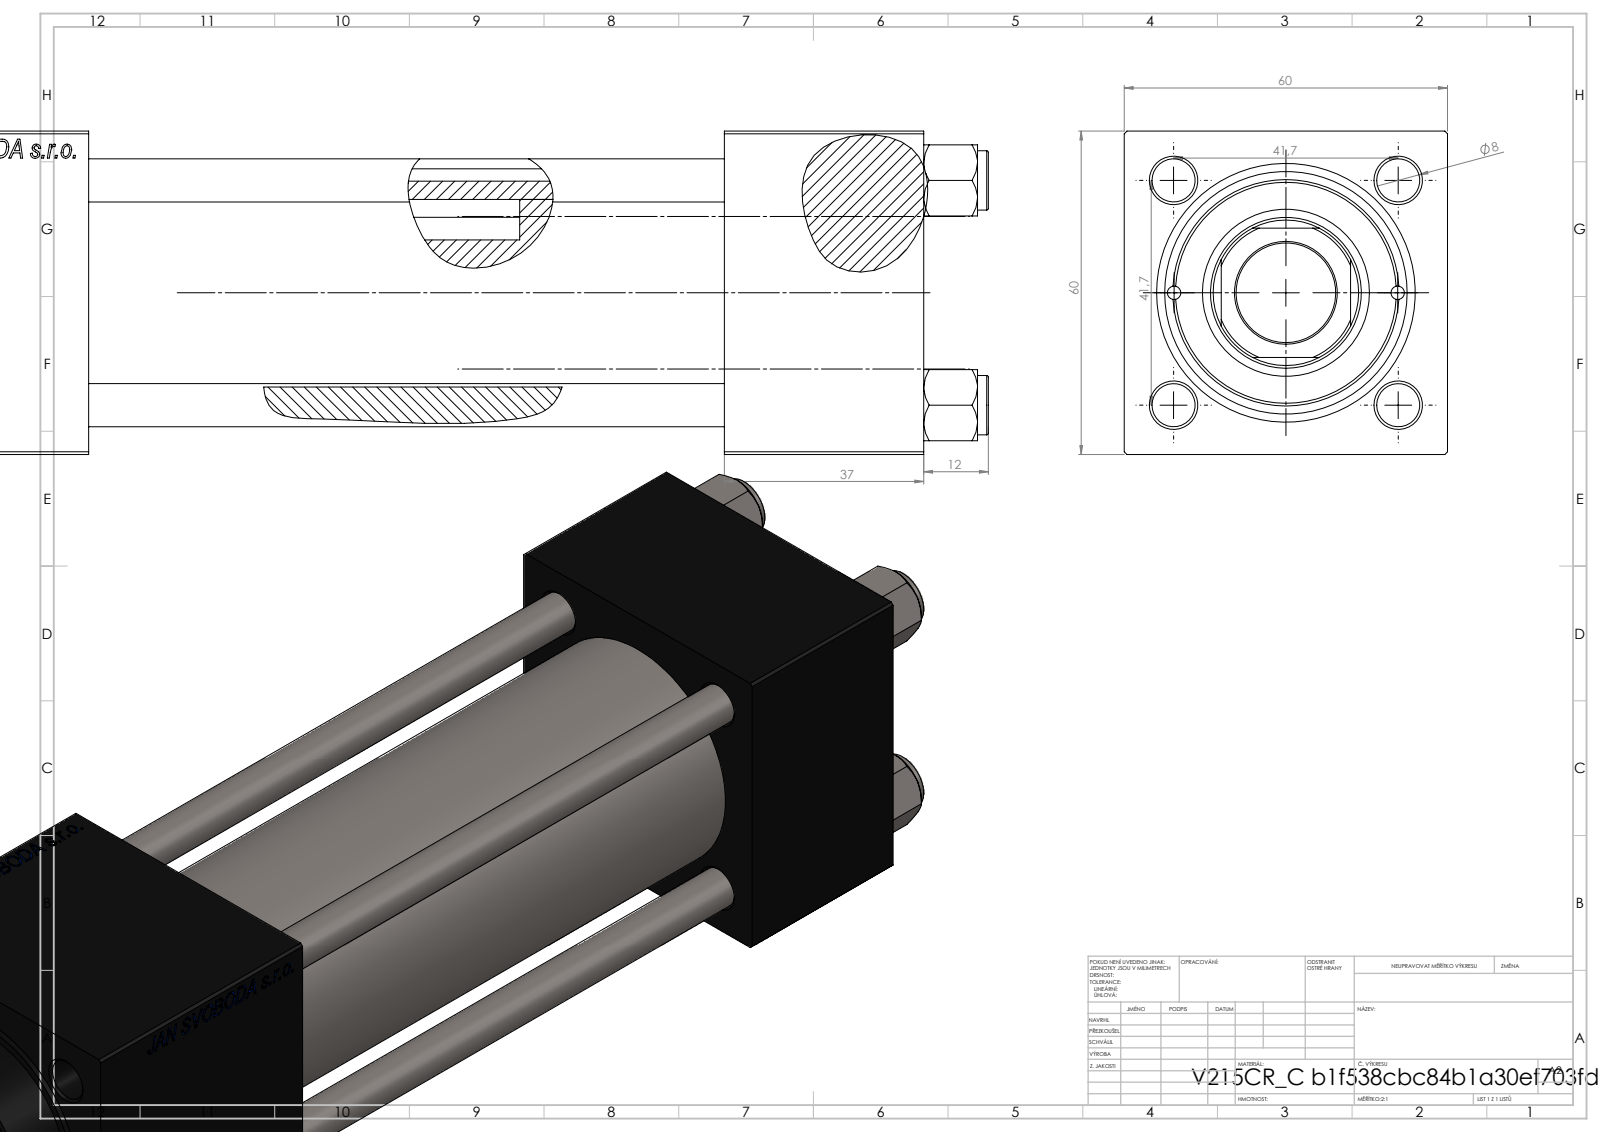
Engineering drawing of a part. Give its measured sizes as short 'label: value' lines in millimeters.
name: V215CR_C_TYCINKA; V215CR_VCP_C; NUT_M5_C; V215_VC_A (+1 more)
written by: SolidWorks 2019 (CONFIG_CONTROL_DESIGN)
unit: mm
bodies: 11 solids, 1154 faces (528 planar, 90 cylindrical, 536 other)
size: 245 × 60 × 60
volume: 497 387 mm³; area: 139 077 mm²
holes: 4× ⌀8, 2× ⌀2.5, 2× ⌀7, 2× ⌀16.66, 2× ⌀24, 1× ⌀18.5, 1× ⌀28, 1× ⌀31, 1× ⌀40, 1× ⌀45
bosses: 4× ⌀11, 1× ⌀46, 1× ⌀42
rounds: 1× R13.5
face distances: 60, 37, 155, 118, 179.3, 142.3, 24.3, 53, 208, 171
hole spacings: 20.85, 29.49, 41.7, 46.53, 20.75, 58.97, 41.5, 152.5
